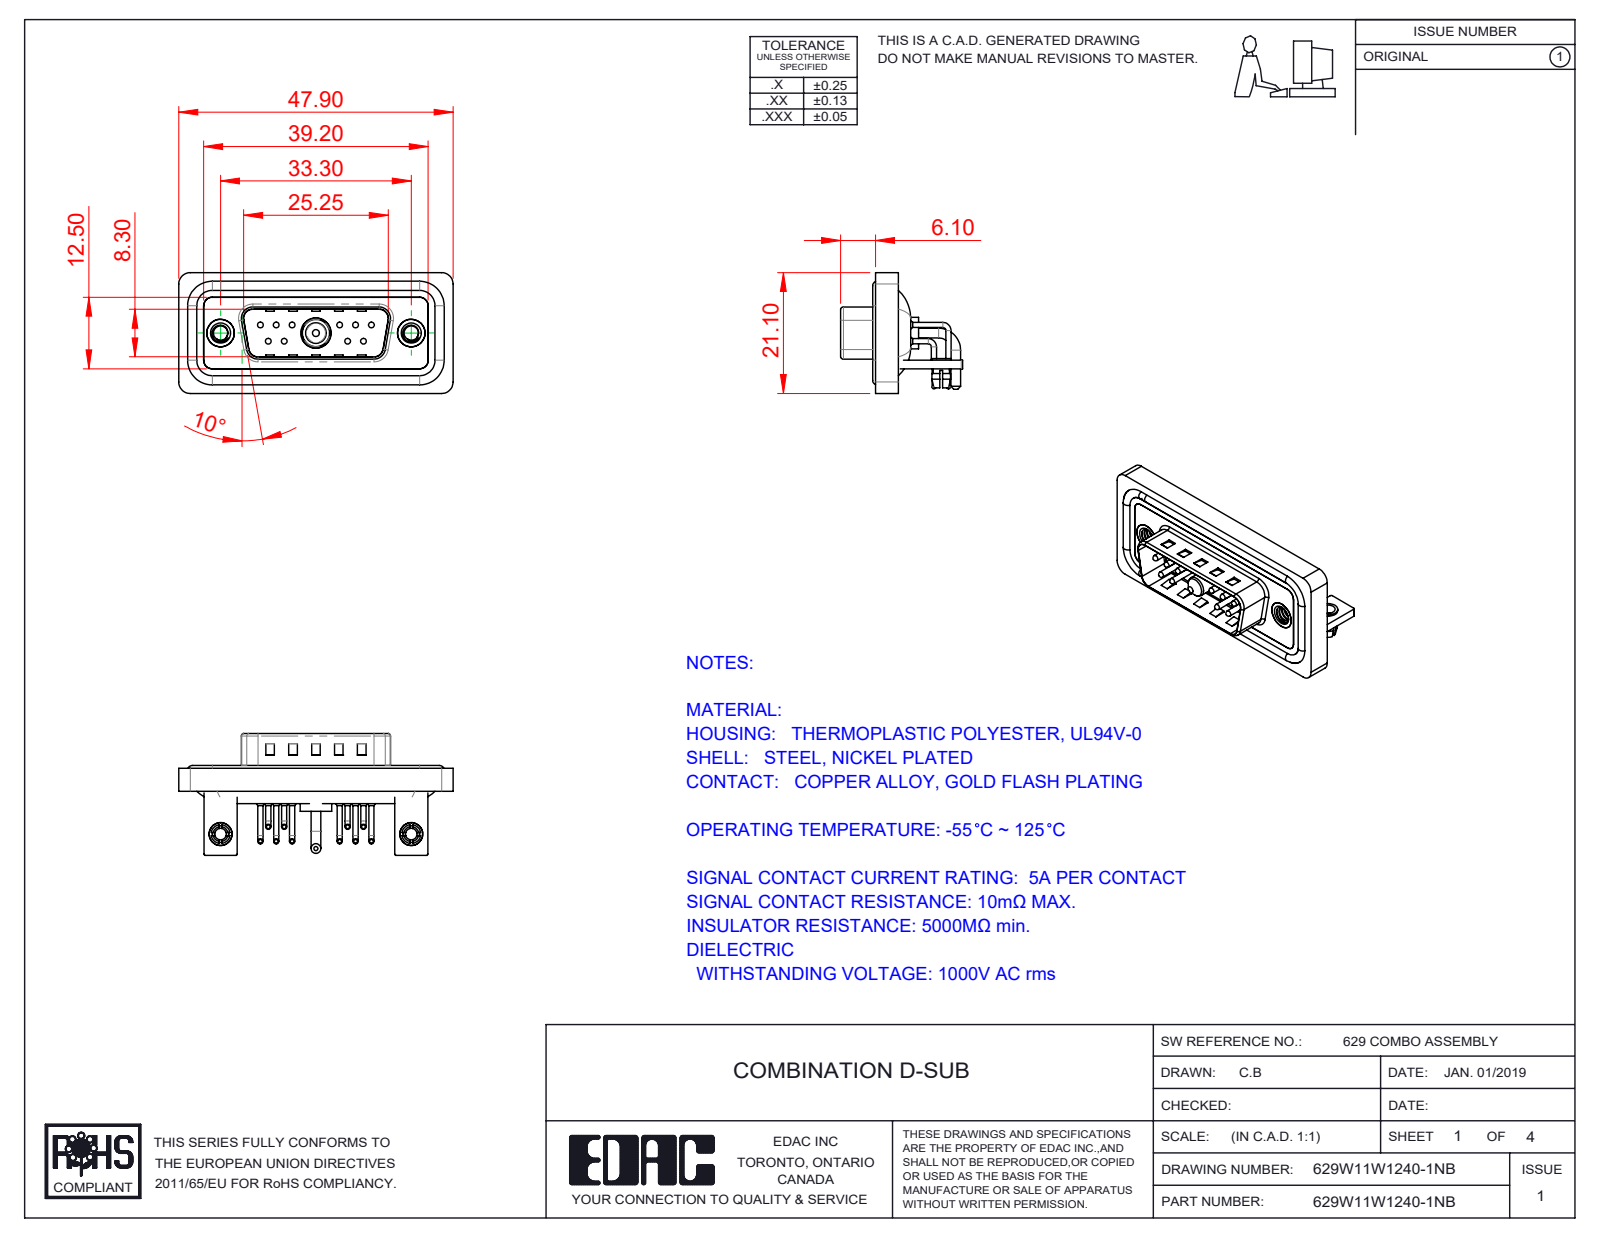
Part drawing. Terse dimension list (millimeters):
name: 629Combo Threaded Rivet_B; 629Combo Contact Row 2; 629Combo Contact Row 1; 629Combo Waterproof Housing_15 Contacts (+7 more)
written by: SolidWorks 2020 (CONFIG_CONTROL_DESIGN)
unit: mm
bodies: 23 solids, 1733 faces (904 planar, 619 cylindrical, 210 other)
size: 47.9 × 21.3 × 21.1
volume: 5 840 mm³; area: 10 028 mm²
holes: 12× ⌀2, 10× ⌀0.75, 10× ⌀1.6, 4× ⌀2.5, 2× ⌀3.2, 2× ⌀4, 2× ⌀4.8, 2× ⌀5, 1× ⌀4.85, 1× ⌀5.3
bosses: 20× ⌀0.9, 10× ⌀1.5, 10× ⌀1, 10× ⌀0.65, 4× ⌀1.6, 2× ⌀4.9, 2× ⌀4, 2× ⌀3.4
rounds: 21× R2, 18× R1.5, 16× R0.25, 10× R1.01, 9× R0.5, 8× R1.6, 7× R1, 4× R0.6
face distances: 0.4, 0.8, 1.5, 2.9, 2.1, 1.1, 1.6, 1.2, 3.7, 4.1
hole spacings: 3.16, 2.77, 13.85, 11.08, 16.62, 5.03, 5.04, 5.54
